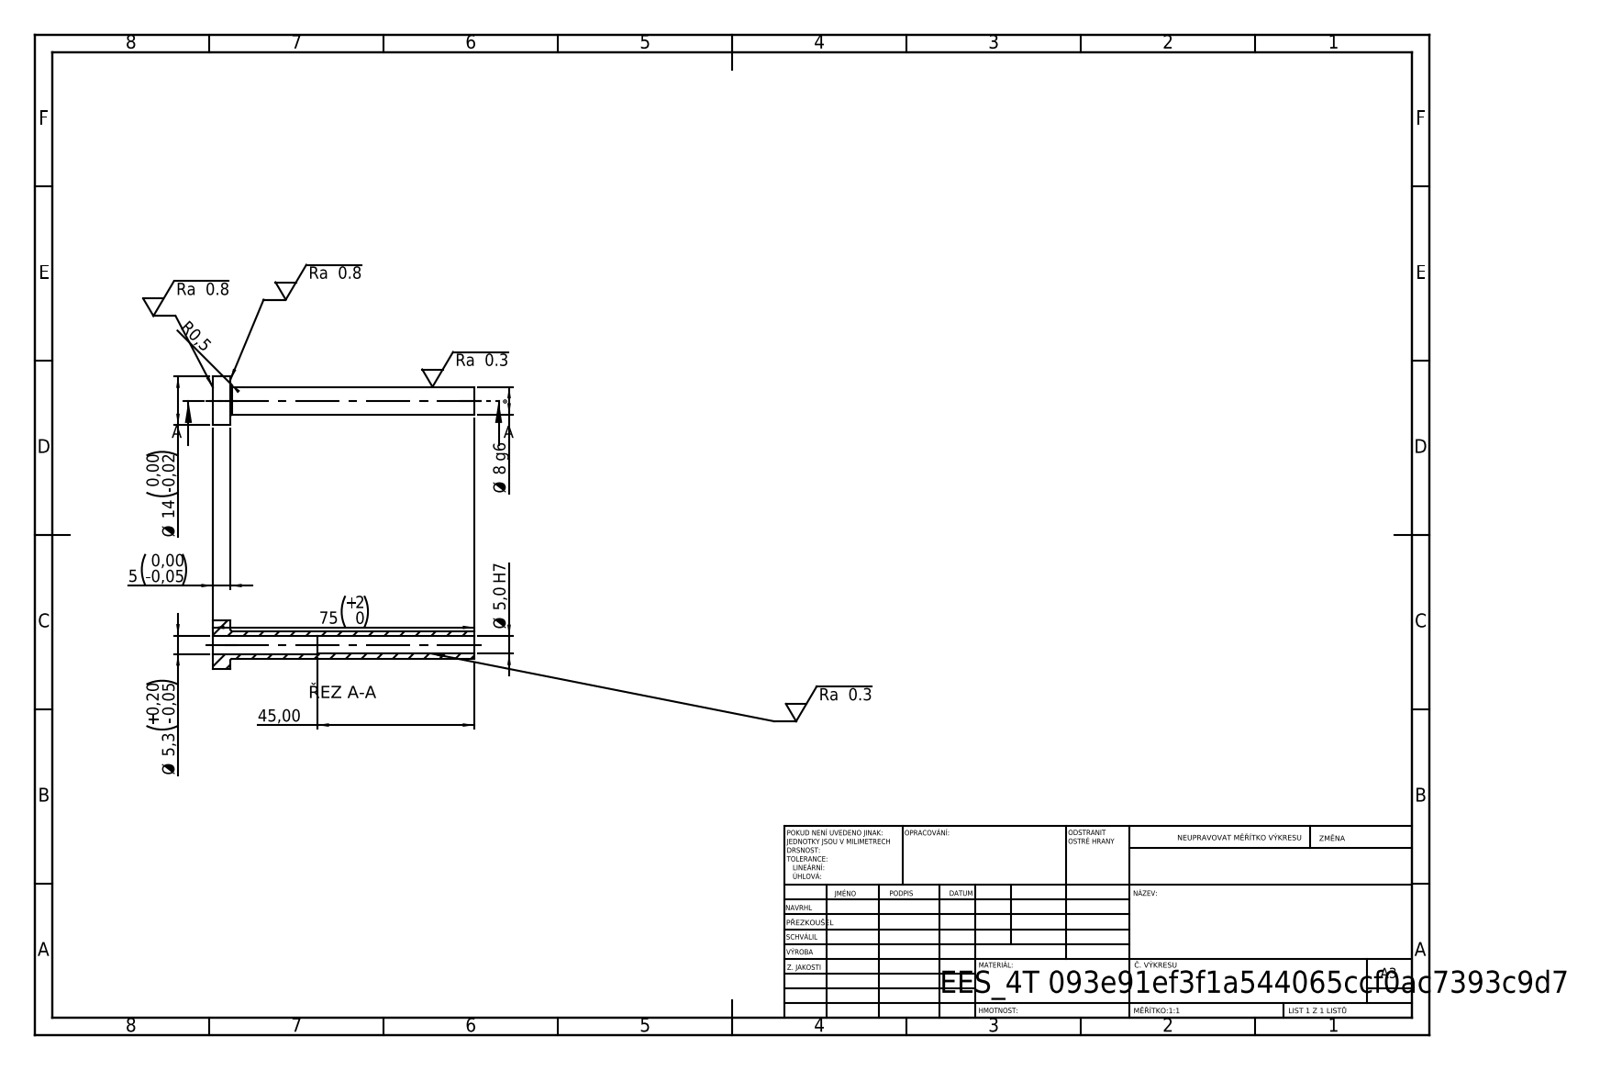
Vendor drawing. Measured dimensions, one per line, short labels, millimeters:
written by: SolidWorks 2019 (CONFIG_CONTROL_DESIGN)
unit: mm
bodies: 1 solid, 14 faces (4 planar, 8 cylindrical, 2 other)
size: 75 × 14 × 14
volume: 2 744 mm³; area: 3 449 mm²
holes: 1× ⌀5, 1× ⌀5.3
bosses: 1× ⌀14, 1× ⌀8
face distances: 5, 75, 70, 30, 25, 45
